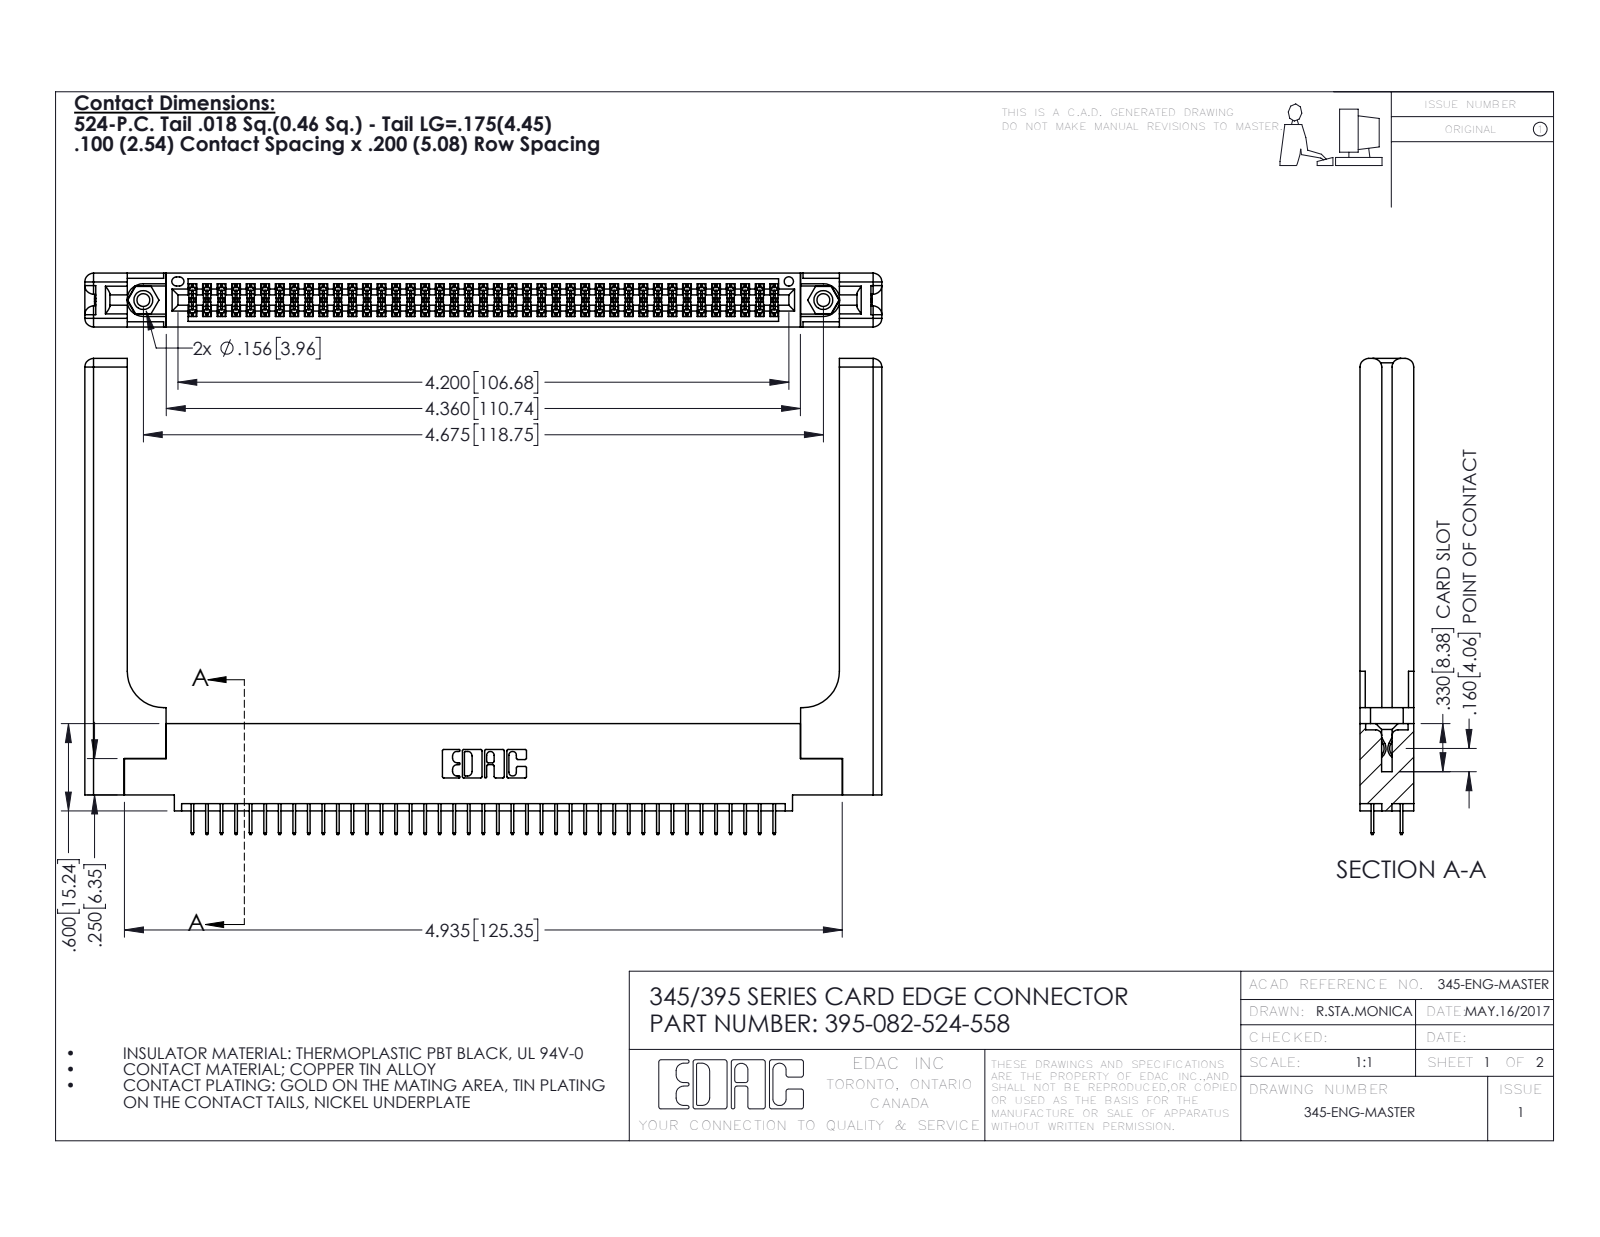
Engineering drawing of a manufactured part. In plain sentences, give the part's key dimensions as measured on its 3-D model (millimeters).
The part is named "345-250-001_345-250-001-102; 345-292-001_345-293-124; 345 Part_0.110 Offset - 0.156 Dia-TH; 395-082-524-558 (+1 more)". Its 3-D file was written by "SolidWorks 2016 (CONFIG_CONTROL_DESIGN)". It is 87 solids with 4814 faces: 3430 planar, 1324 cylindrical and 60 other. Overall it measures 139.2 by 83.1 by 9.4 millimeters. Its volume is 21 790 cubic millimeters and its surface area 24 480 square millimeters. Round holes: 2 of diameter 2.3, 2 of diameter 3.2, 2 of diameter 4, 1 of diameter 1.6. Round bosses or shafts: 2 of diameter 3.9. Partial cylindrical surfaces (rounded edges, fillets, slot ends): 123 of radius 0.2, 22 of radius 0.3, 16 of radius 1.5, 6 of radius 0.2, 6 of radius 0.8, 3 of radius 0.7, 2 of radius 0.4, 2 of radius 0.5. The main face-to-face distances are 9.4, 1.8, 7.6, 5.1, 2.5, 6.9, 0.6, 5.7, 3.8, 3.8. The hole center spacings are 6.9, 112.8, 118.7.
